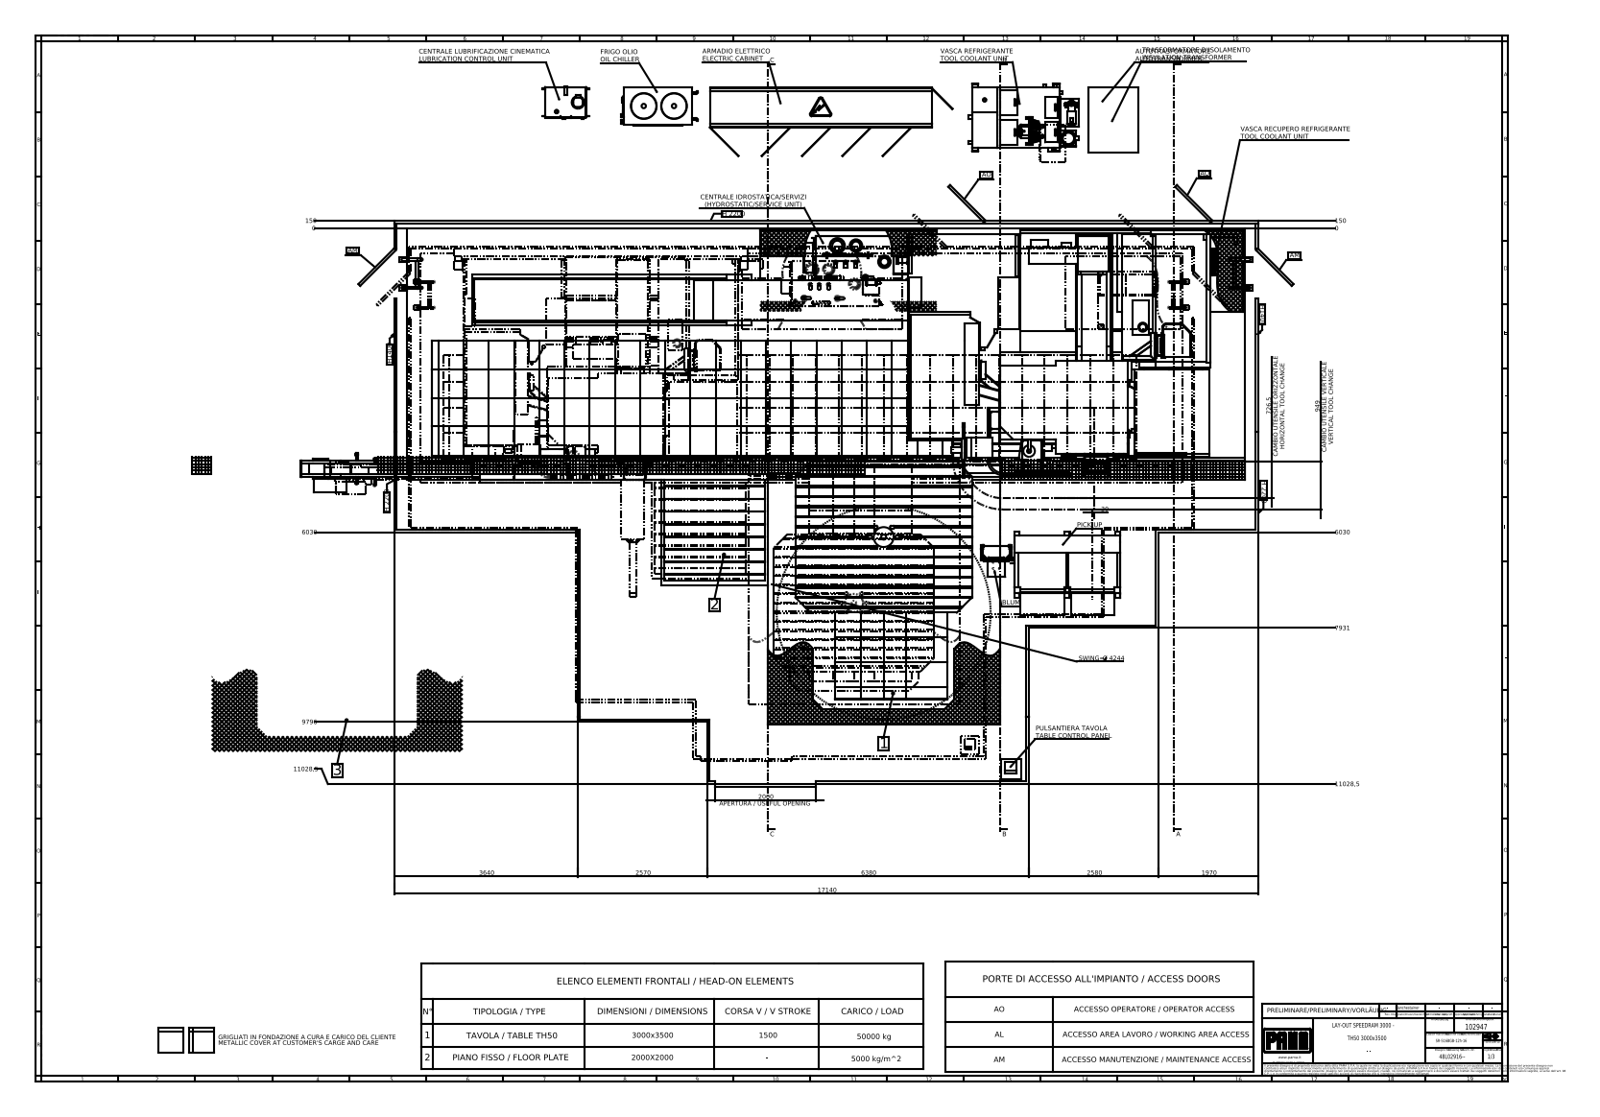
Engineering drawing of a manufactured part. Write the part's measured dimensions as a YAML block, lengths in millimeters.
part_name: "S003390; S003412_H=1000; S003304; S003282_X=MIN; Y=MIN; Z=MIN; W=MIN (+8 more)"
step_written_by: "SolidWorks 2023 (AUTOMOTIVE_DESIGN)"
units: millimeters
bodies: {solids: 508, faces: 8365, planar: 5792, cylindrical: 2039, other: 534}
overall_size: [20640, 16849.9, 10174]
volume: 614900000000
surface_area: 2322000000
round_holes:
  - {diameter: 35, count: 128}
  - {diameter: 69.6, count: 123}
  - {diameter: 37.2, count: 18}
  - {diameter: 30, count: 9}
  - {diameter: 13, count: 8}
  - {diameter: 14, count: 8}
  - {diameter: 8, count: 6}
  - {diameter: 340, count: 5}
  - {diameter: 12.5, count: 4}
  - {diameter: 56.66, count: 4}
  - {diameter: 60, count: 4}
  - {diameter: 25.6, count: 3}
round_bosses_or_shafts:
  - {diameter: 42.4, count: 18}
  - {diameter: 20, count: 14}
  - {diameter: 40, count: 11}
  - {diameter: 150, count: 10}
  - {diameter: 9, count: 10}
  - {diameter: 60, count: 9}
  - {diameter: 55, count: 8}
  - {diameter: 66.3, count: 7}
partial_cylinders:
  - {radius: 5, count: 180}
  - {radius: 15, count: 93}
  - {radius: 35, count: 62}
  - {radius: 8, count: 52}
  - {radius: 6, count: 28}
  - {radius: 10, count: 28}
  - {radius: 20, count: 24}
  - {radius: 3, count: 23}
face_to_face_distances: [2000, 50, 720, 1280, 10, 16778.5, 2650, 2700, 14128.5, 14078.5]
hole_center_spacings: [273.13, 500, 1431.99, 758.02, 1597.06, 1000, 130, 1254.83]
